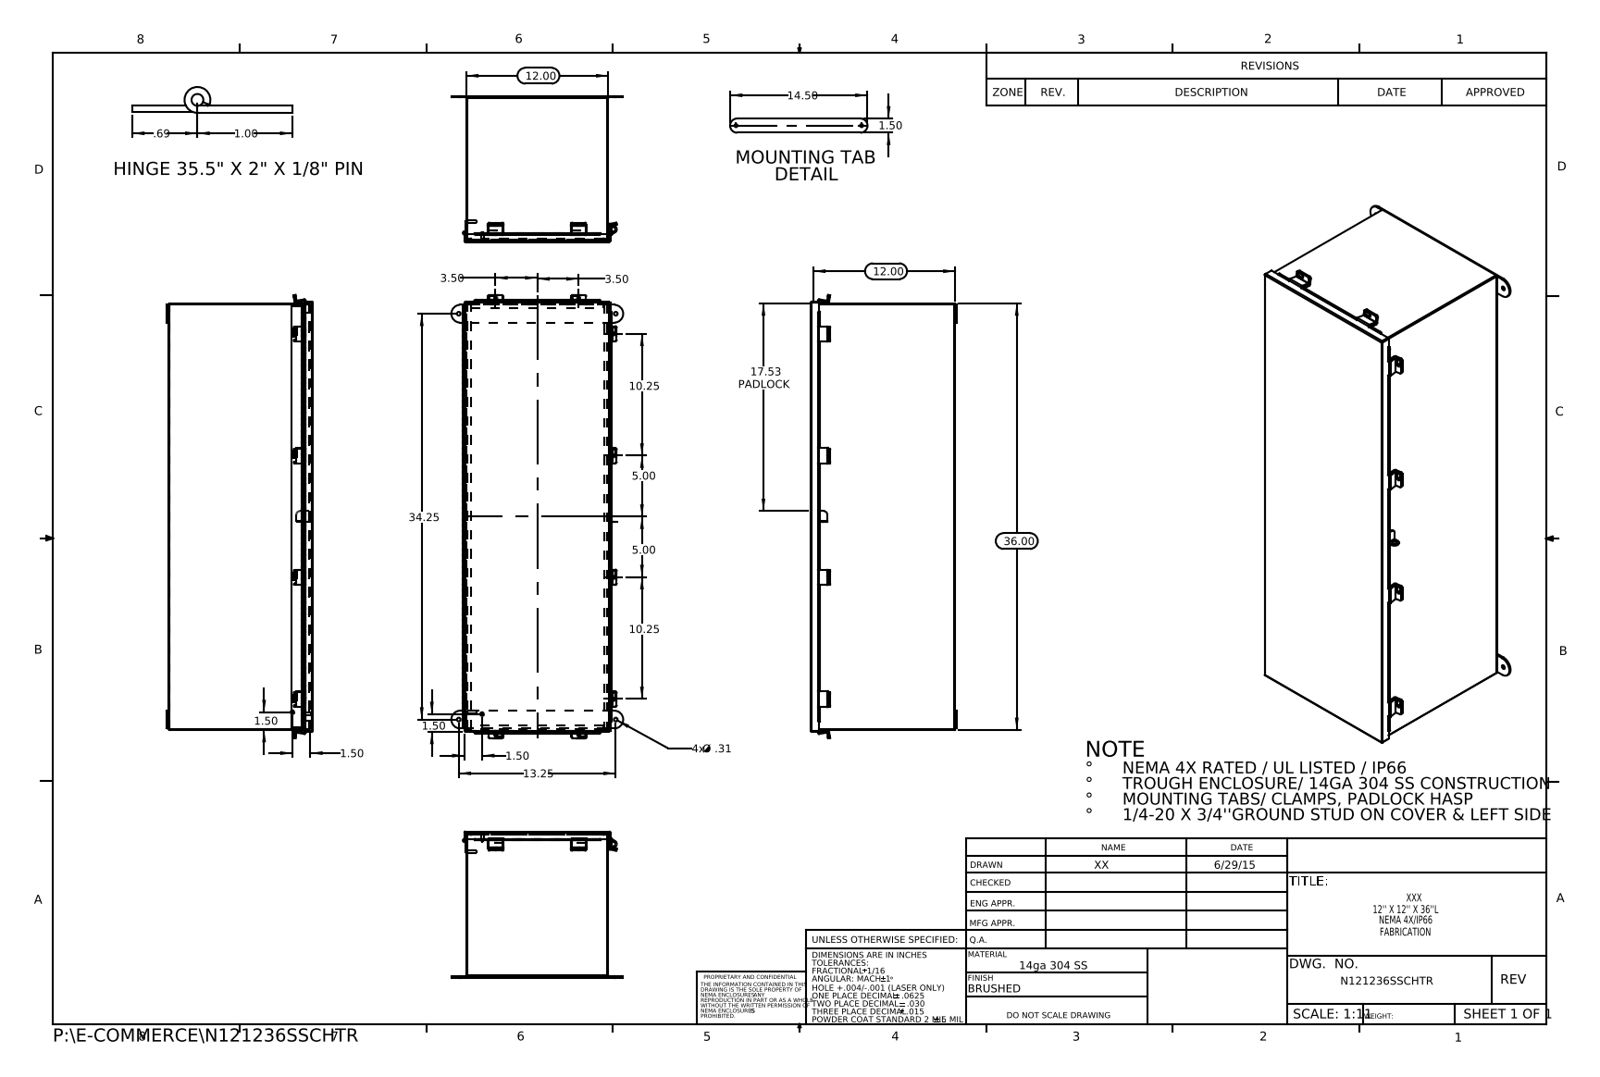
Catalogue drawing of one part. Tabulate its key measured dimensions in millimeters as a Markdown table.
| quantity | value |
| --- | --- |
| part name | N121236SSCHTR JIC Top; N121236SSCHTR JIC Cover Clamp; N121236SSCHTR JIC Clamp Bracket; N121236SSCHTR JIC_Cover_Template (+8 more) |
| STEP written by | SolidWorks 2015 (CONFIG_CONTROL_DESIGN) |
| units | millimeters |
| bodies | 27 solids, 1240 faces (761 planar, 459 cylindrical, 20 other) |
| overall size | 950.1 × 368.3 × 313.4 |
| volume | 2 789 000 mm³ |
| surface area | 2 936 000 mm² |
| round holes (diameter × count) | 6.4 × 8, 8 × 4, 3.2 × 1, 9.5 × 1 |
| round bosses / shafts (diameter × count) | 8 × 2, 6 × 2, 6.9 × 1, 6.4 × 1 |
| partial cylindrical surfaces (radius × count) | 3.2 × 28, 3.4 × 16, 0.2 × 12, 0.3 × 11, 2.2 × 11, 2.1 × 6, 2.5 × 6, 19.1 × 4 |
| main face-to-face distances | 1.9, 302.9, 308.1, 304.8, 301, 310, 306.1, 912.5, 910.6, 914.4 |
| hole center spacings | 177.8, 261.3, 336.6, 522.3, 870, 932.8, 261, 318.5 |
